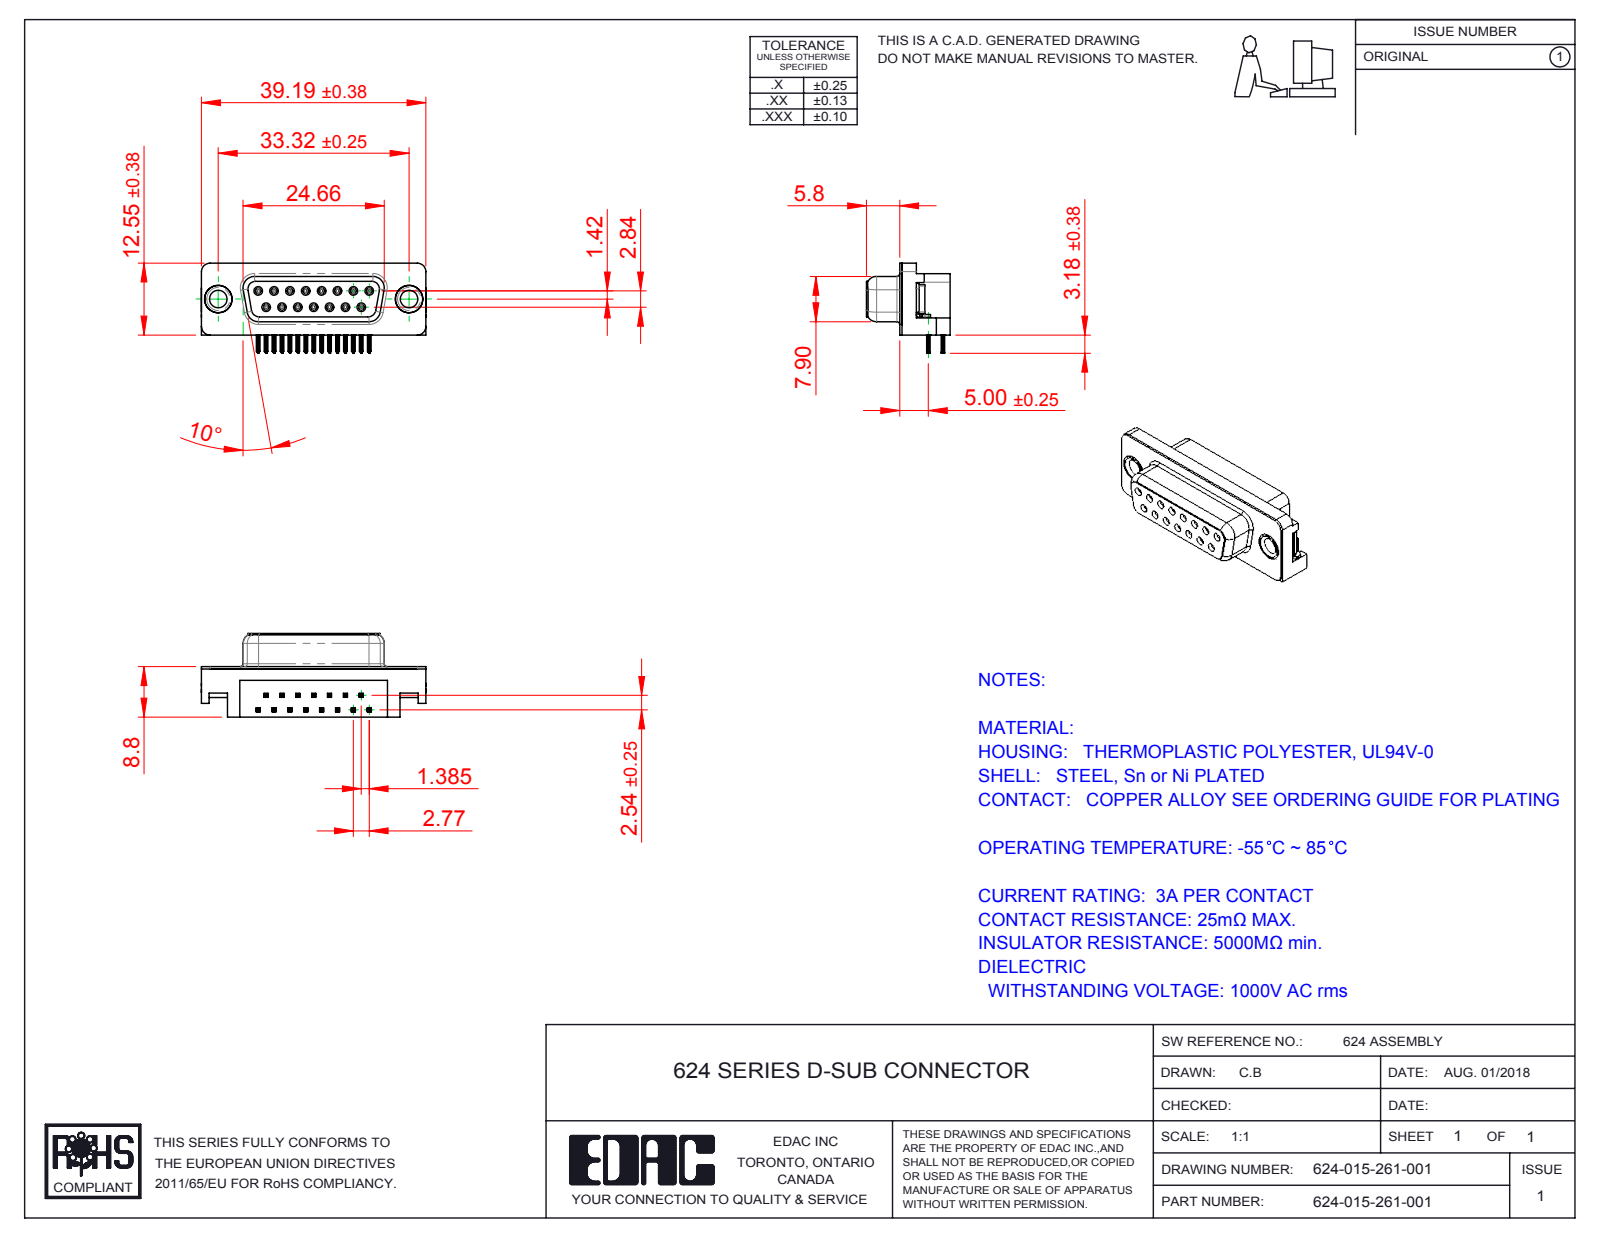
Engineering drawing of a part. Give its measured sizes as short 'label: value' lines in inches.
name: 624-015-261-001; 624 Housing_15 Socket; 624 Shell_15 Socket; 624 Socket Bottom (+3 more)
written by: SolidWorks 2016 (CONFIG_CONTROL_DESIGN)
unit: in
bodies: 21 solids, 2305 faces (1002 planar, 577 cylindrical, 726 other)
size: 1.544 × 0.619 × 0.575
volume: 0.248 in³; area: 8.945 in²
holes: 15× ⌀0.031, 15× ⌀0.035, 2× ⌀0.12, 2× ⌀0.157, 2× ⌀0.189, 2× ⌀0.197
bosses: 15× ⌀0.047, 2× ⌀0.193, 2× ⌀0.187, 2× ⌀0.152
rounds: 120× R0.004, 60× R0.006, 30× R0.014, 18× R0.039, 15× R0.013, 8× R0.01, 8× R0.053, 8× R0.059
face distances: 0.016, 0.331, 0.244, 0.346, 0.369, 0.125, 0.114, 0.232, 0.098, 0.107
hole spacings: 0.124, 0.109, 0.218, 0.327, 0.436, 0.198, 0.198, 0.294
